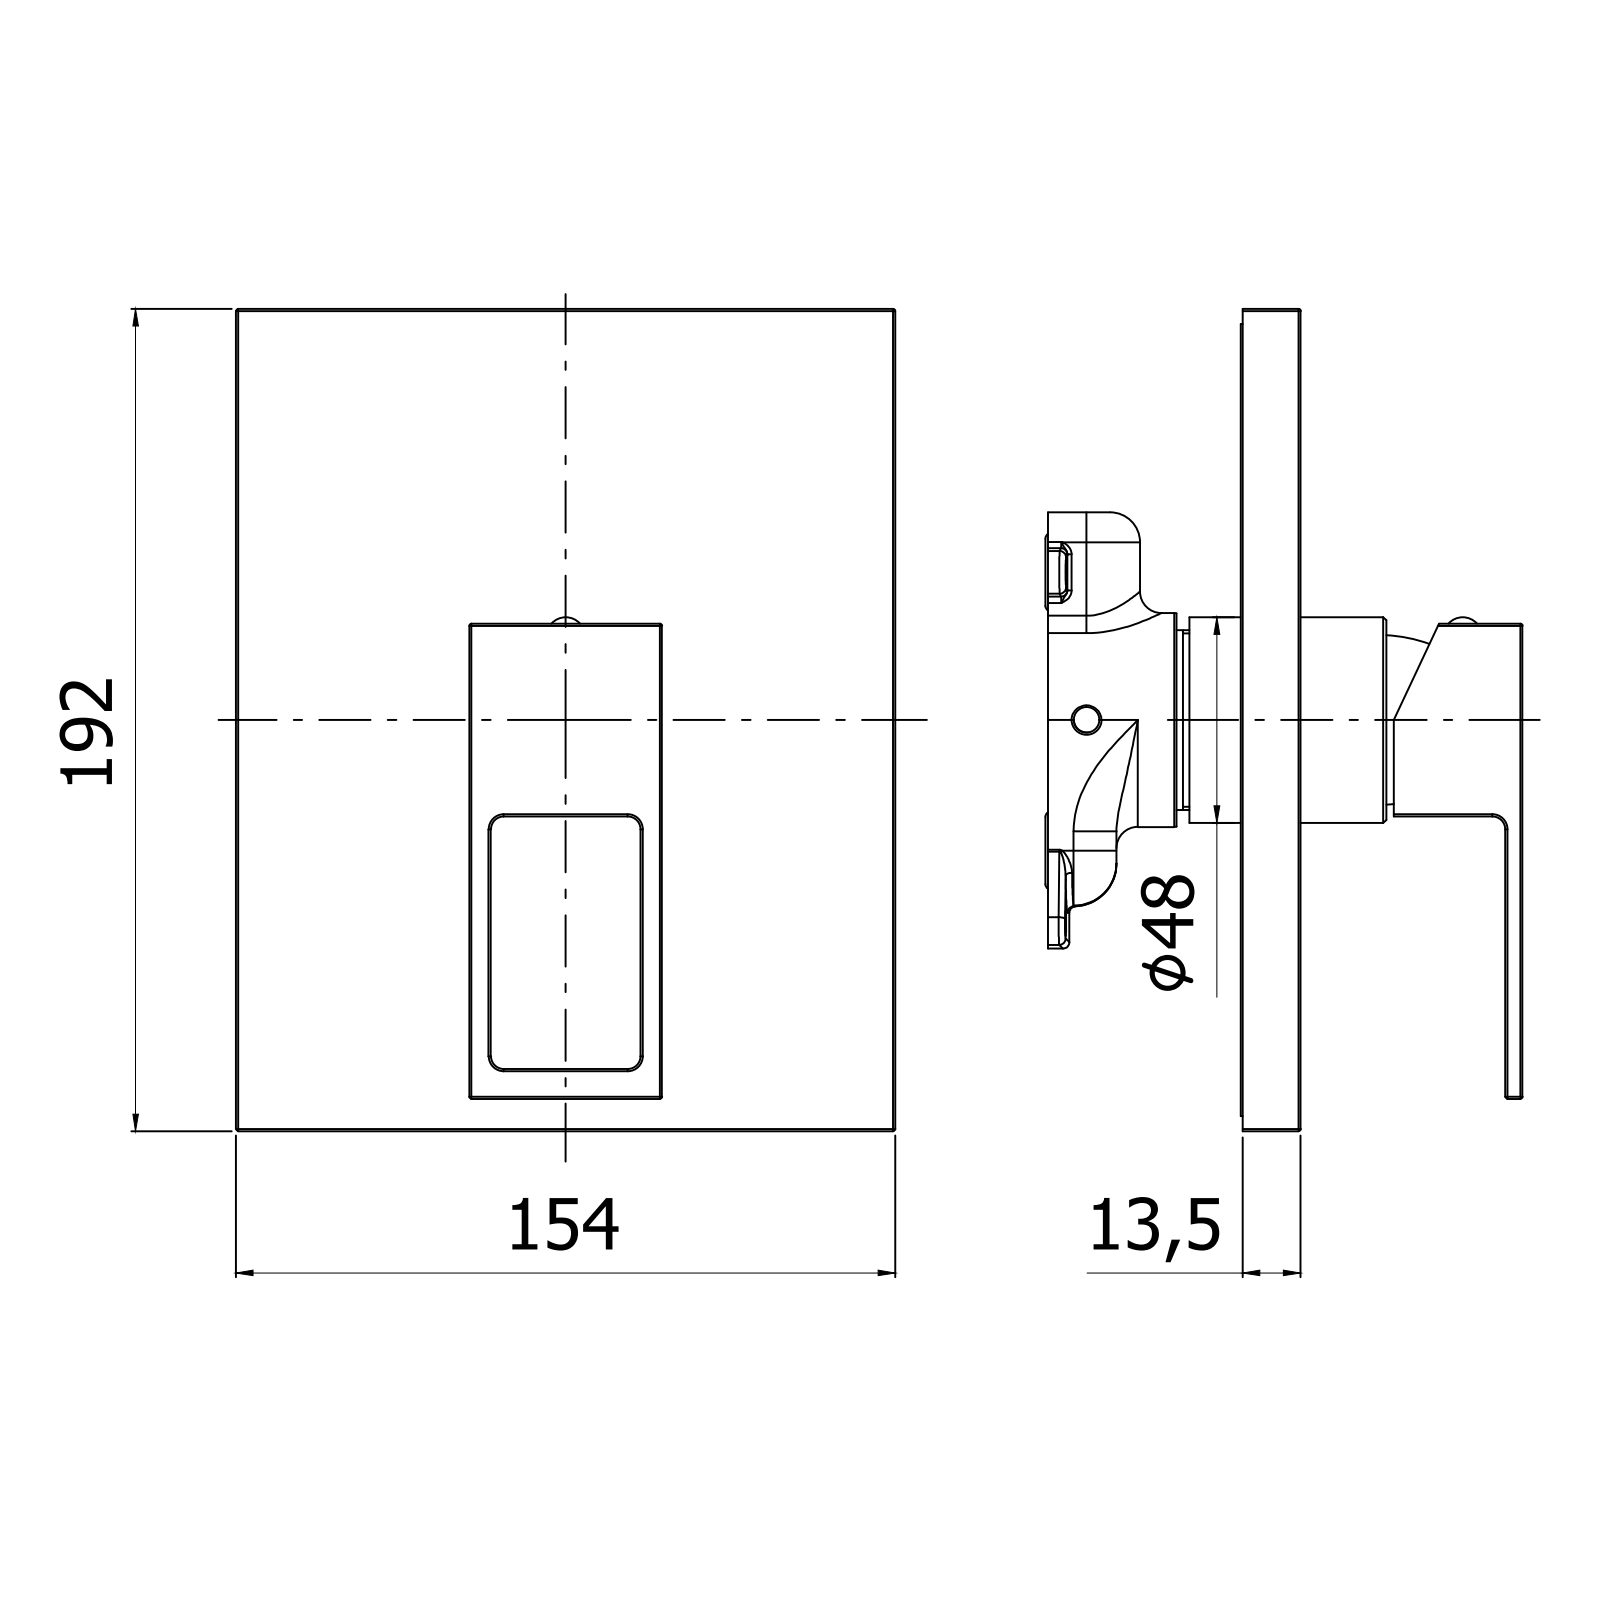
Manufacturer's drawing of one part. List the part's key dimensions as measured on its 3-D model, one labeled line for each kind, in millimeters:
Part name (STEP PRODUCT): EFBOX010CR
STEP written by: CREO PARAMETRIC BY PTC INC, 2020044 (CONFIG_CONTROL_DESIGN)
Units: millimetres
Bodies: 2 solids, 1023 faces (627 planar, 257 cylindrical, 139 other)
Overall size (bounding box): 192 × 154 × 65.6
Volume: 296 580 mm³ · Surface area: 121 662 mm²
Round holes (diameter × count): ⌀5 ×3, ⌀7 ×3, ⌀2 ×2, ⌀4 ×2, ⌀3 ×1, ⌀4.5 ×1, ⌀5.5 ×1, ⌀7.8 ×1, ⌀19.5 ×1, ⌀19.9 ×1, ⌀26.8 ×1, ⌀29 ×1
Round bosses / shafts (diameter × count): ⌀4.8 ×2, ⌀57 ×1, ⌀48.1 ×1, ⌀39 ×1, ⌀35 ×1, ⌀34.8 ×1, ⌀32.2 ×1, ⌀23.5 ×1
Partial cylindrical surfaces — rounded edges, fillets, slot ends (radius × count): R0.5 ×51, R0.15 ×11, R3 ×5, R0.3 ×4, R1 ×2, R2.5 ×1, R4 ×1, R7 ×1
Main face-to-face distances: 3, 13.5, 10.5, 23.5, 52.1, 31, 130.5, 99.5, 54.5, 76
Hole centre spacings: 8.6, 13.45, 15.13, 21.93, 9.5, 14, 18
